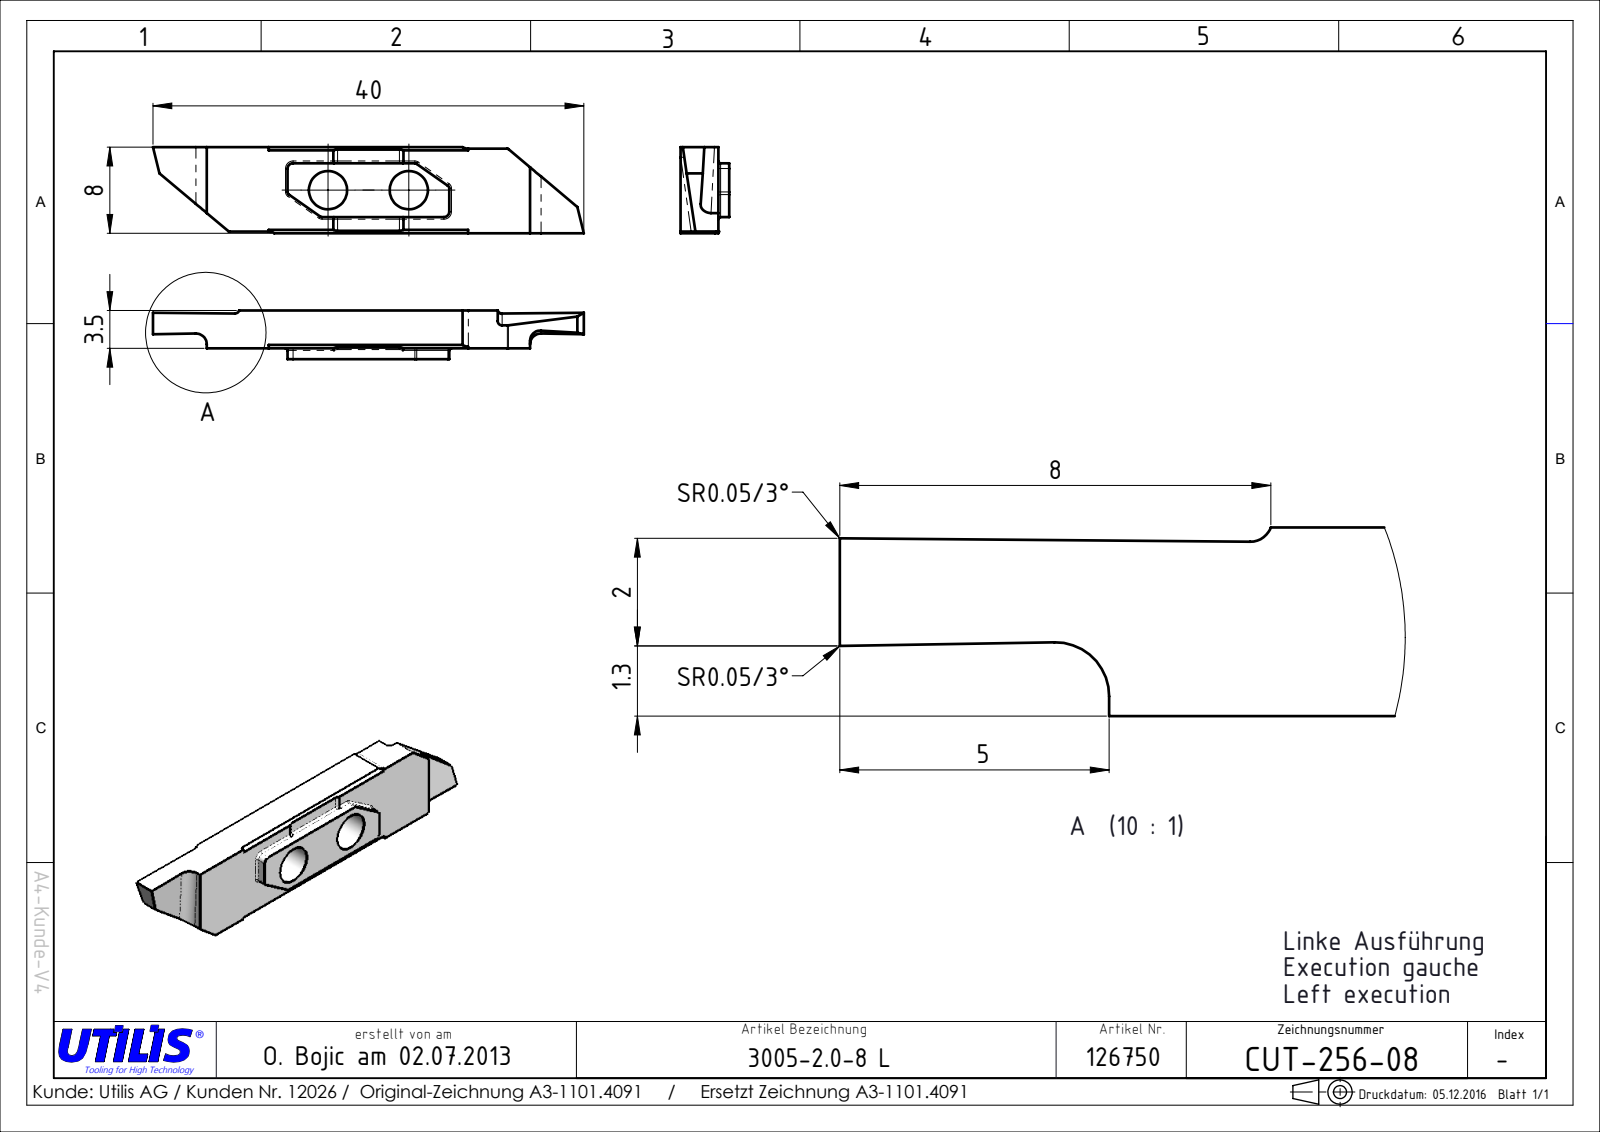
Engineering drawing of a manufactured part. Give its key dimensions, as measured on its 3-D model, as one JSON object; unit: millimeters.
{"part_name": "CUT-256-08", "step_written_by": "SolidWorks 2016 (AUTOMOTIVE_DESIGN)", "units": "millimeters", "bodies": {"solids": 1, "faces": 38, "planar": 24, "cylindrical": 14, "other": 0}, "overall_size": [40, 8, 3.5], "volume_mm3": 819, "surface_area_mm2": 859, "round_holes": [[3.55, 2]], "partial_cylinders_radius": [[0.15, 4], [1, 4], [0.4, 2]], "face_to_face_distances": [3.5, 8, 7.85, 22.54, 7.7, 5, 35, 40, 30, 38.98], "hole_center_spacings": [7.5]}
